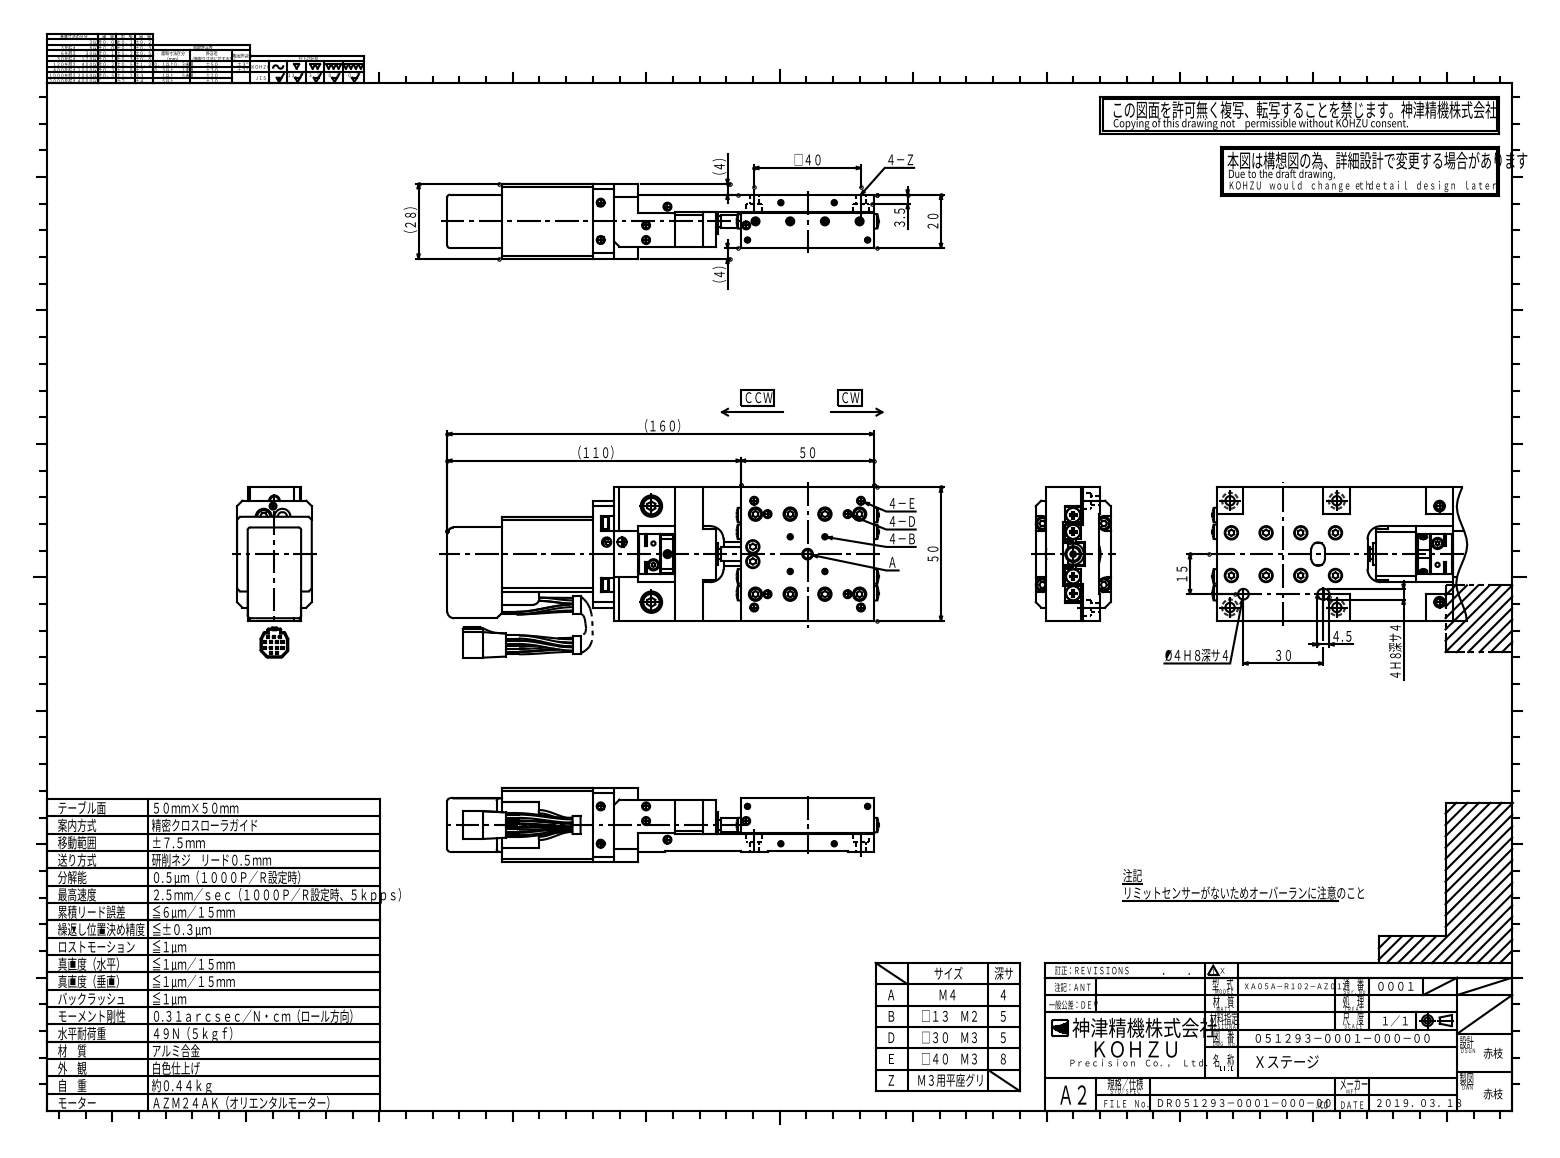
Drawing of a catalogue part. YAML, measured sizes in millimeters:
part_name: "DR051293-0001-000-00-prt0; DR051293-0001-000-00-prt1; DR051293-0001-000-00-prt2; DR051293-0001-000-00-prt3 (+2 more)"
step_written_by: "spGate 13.4.4 (AUTOMOTIVE_DESIGN)"
units: millimeters
bodies: {solids: 6, faces: 2235, planar: 1163, cylindrical: 604, other: 468}
overall_size: [161.59, 63.77, 28]
volume: 123719
surface_area: 54102
round_holes:
  - {diameter: 3, count: 25}
  - {diameter: 2.6, count: 20}
  - {diameter: 5, count: 19}
  - {diameter: 2, count: 11}
  - {diameter: 3.5, count: 9}
  - {diameter: 1.6, count: 8}
  - {diameter: 6, count: 8}
  - {diameter: 2.46, count: 7}
  - {diameter: 4, count: 6}
  - {diameter: 1.57, count: 4}
  - {diameter: 2.01, count: 4}
  - {diameter: 2.5, count: 4}
round_bosses_or_shafts:
  - {diameter: 4.5, count: 22}
  - {diameter: 0.97, count: 10}
  - {diameter: 7, count: 4}
  - {diameter: 5, count: 4}
  - {diameter: 3.8, count: 4}
  - {diameter: 3.5, count: 4}
  - {diameter: 2, count: 4}
  - {diameter: 1.23, count: 4}
partial_cylinders:
  - {radius: 1, count: 18}
  - {radius: 0.5, count: 8}
  - {radius: 0.3, count: 6}
  - {radius: 2.5, count: 5}
  - {radius: 0.61, count: 4}
  - {radius: 2.75, count: 4}
  - {radius: 1.07, count: 2}
  - {radius: 1.23, count: 2}
face_to_face_distances: [0.5, 11, 13, 4, 19.7, 6.5, 13.5, 24, 19.5, 7]
hole_center_spacings: [13, 15.53, 8.5, 12.75, 20.94, 21.5, 23.12, 25.12]
